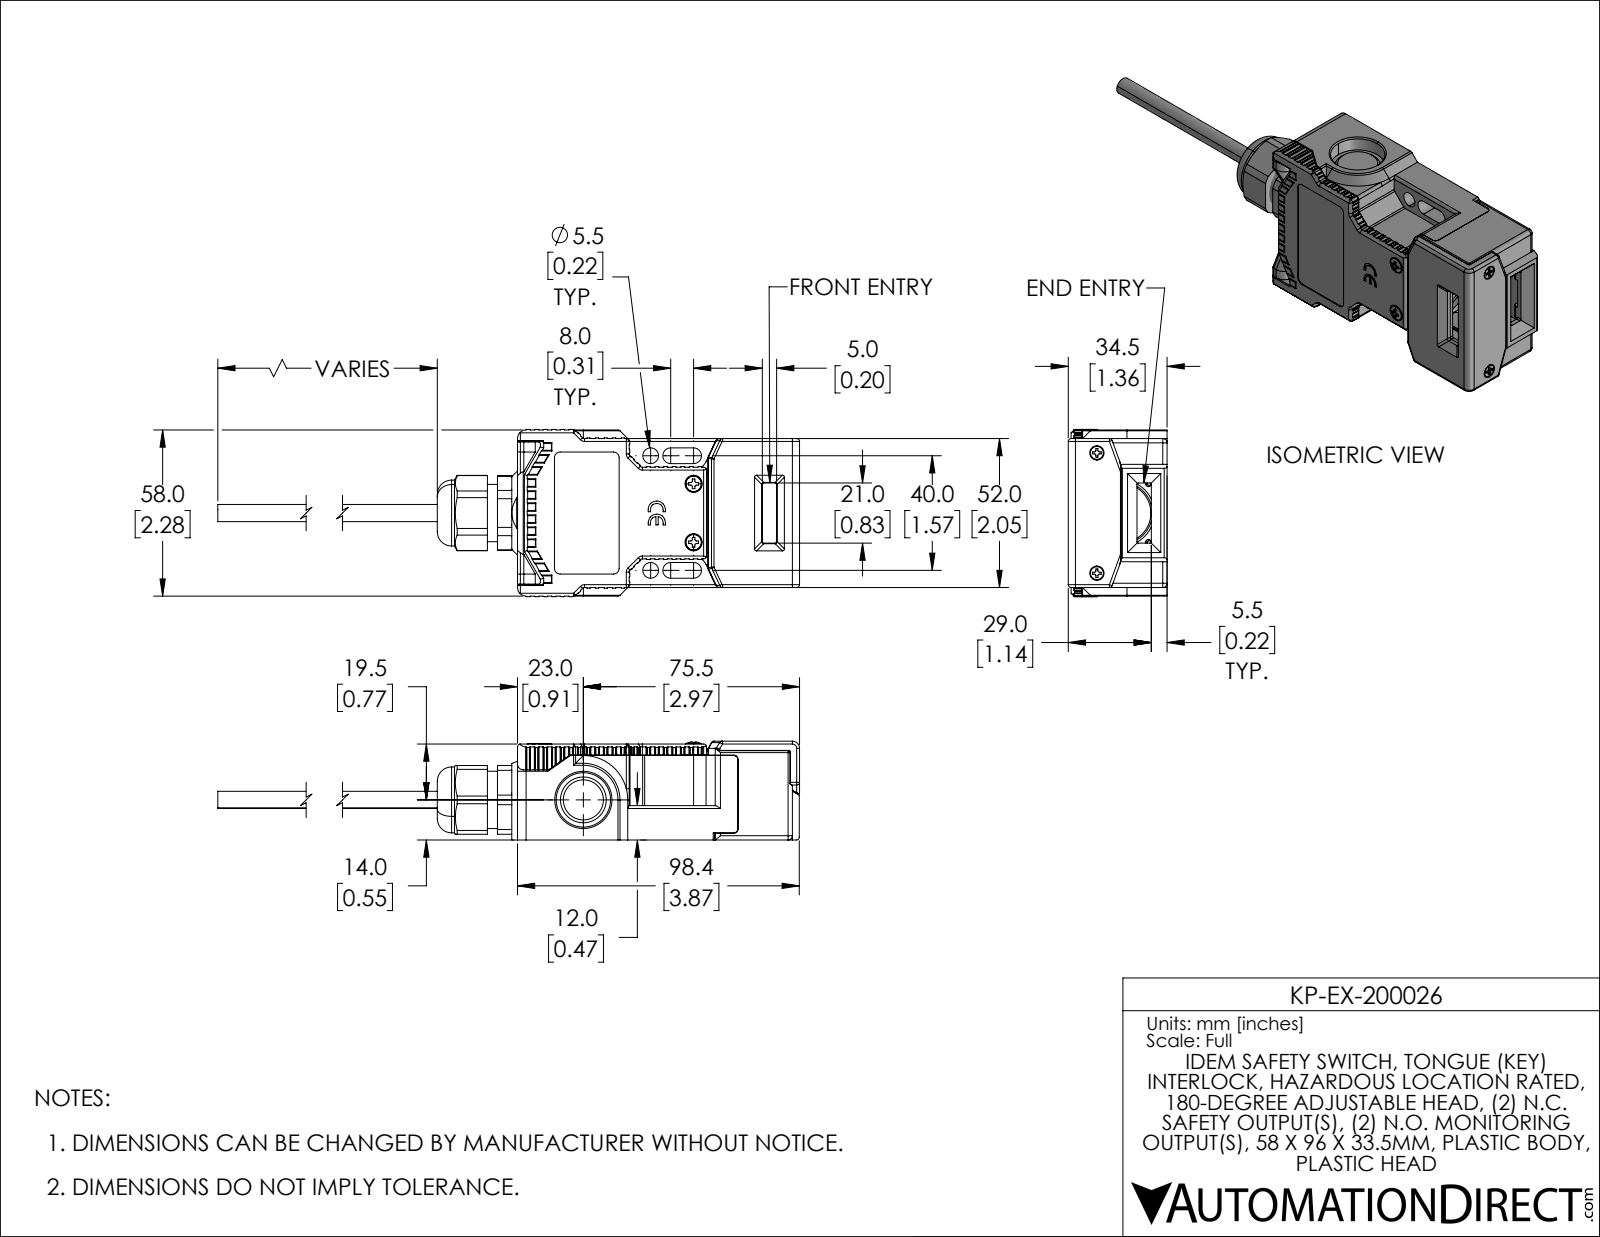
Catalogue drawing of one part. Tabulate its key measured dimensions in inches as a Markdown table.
| quantity | value |
| --- | --- |
| part name | KP-EX-200026 |
| STEP written by | SolidWorks 2021 (AUTOMOTIVE_DESIGN) |
| units | inches |
| bodies | 11 solids, 2891 faces (1495 planar, 1031 cylindrical, 365 other) |
| overall size | 7.539 × 2.299 × 1.358 |
| volume | 5.011 in³ |
| surface area | 106.3 in² |
| round holes (diameter × count) | 0.071 × 4, 0.079 × 4, 0.087 × 3, 0.063 × 2, 0.094 × 2, 0.114 × 2, 0.118 × 2, 0.122 × 2, 0.142 × 2, 0.197 × 2, 0.205 × 2, 0.209 × 2 |
| round bosses / shafts (diameter × count) | 0.276 × 2, 0.22 × 2, 0.213 × 2, 0.197 × 2, 0.177 × 2, 0.11 × 2, 0.071 × 2, 0.906 × 1 |
| partial cylindrical surfaces (radius × count) | 0.012 × 243, 0.02 × 167, 0.004 × 120, 0.039 × 102, 0.008 × 24, 0.059 × 16, 0.079 × 13, 0.047 × 8 |
| main face-to-face distances | 0.098, 0.118, 0.031, 1.26, 0.091, 1.228, 1.167, 0.087, 0.093, 0.059 |
| hole center spacings | 0.195, 1.575, 0.276, 0.398, 0.404, 0.498, 0.516, 0.547 |
